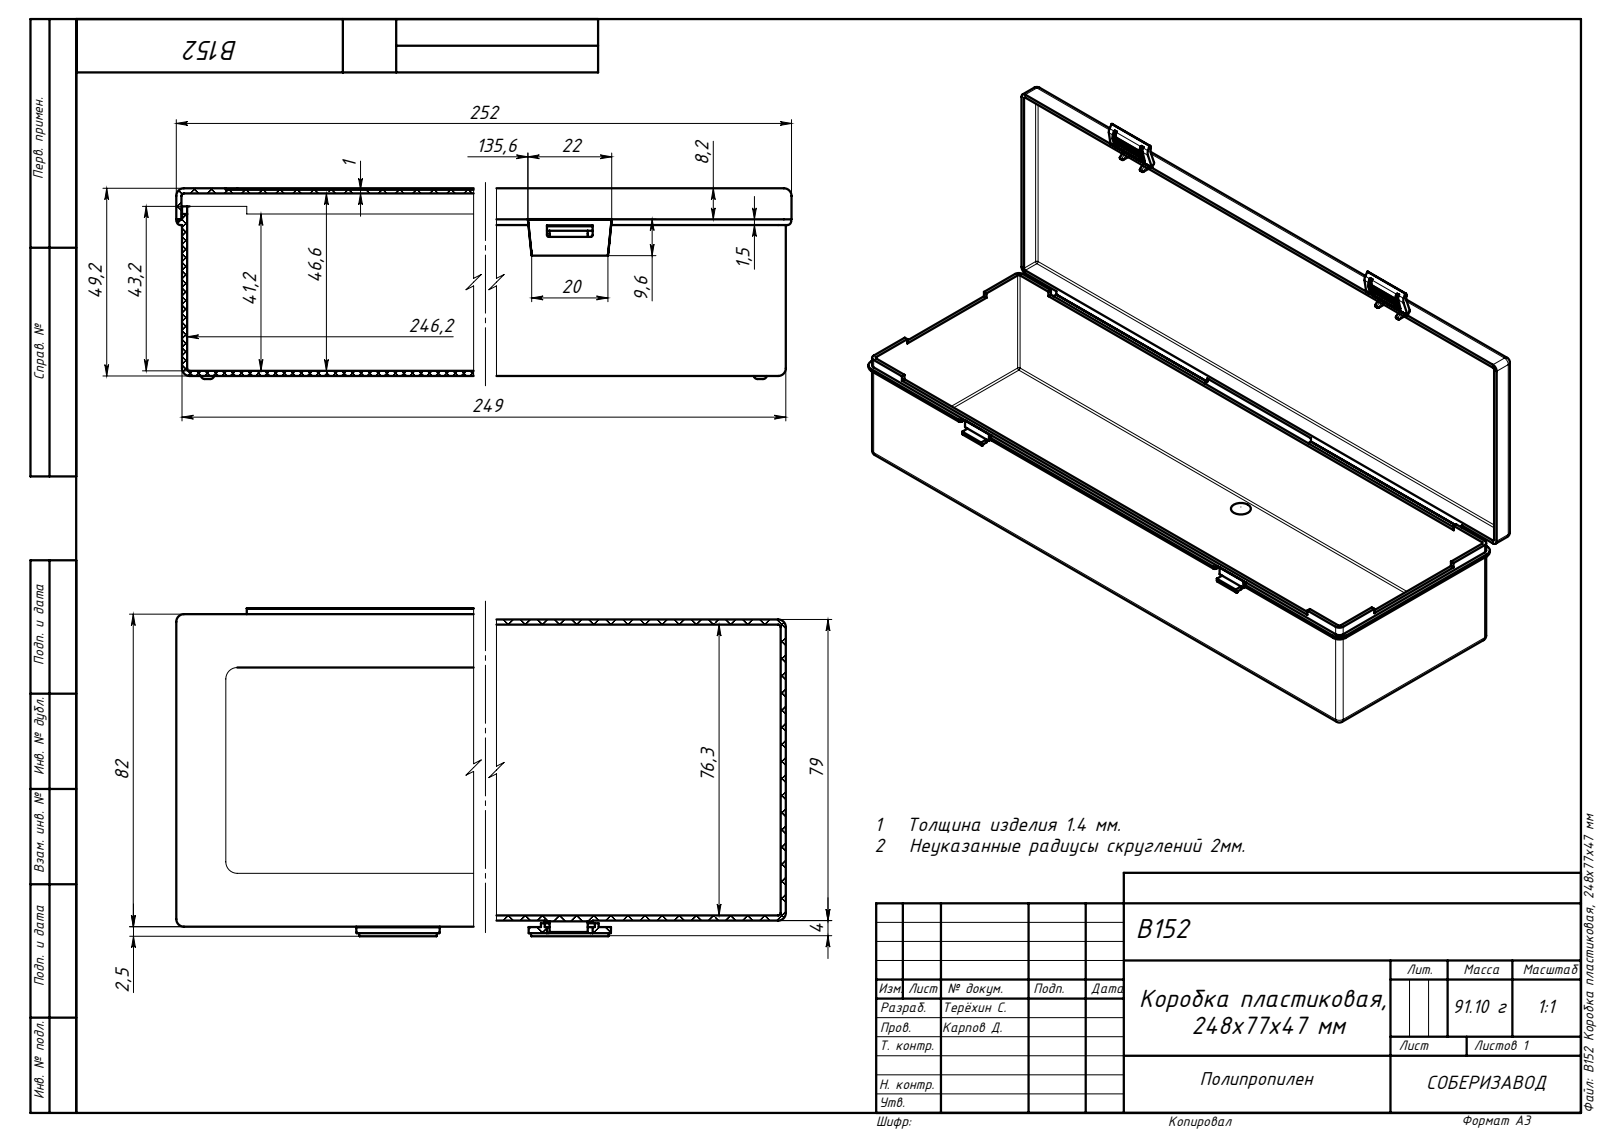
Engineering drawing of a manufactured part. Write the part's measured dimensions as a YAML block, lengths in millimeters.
part_name: "B152 Емкость_00; B152 Коробка пластиковая, 248x77x47 мм; B152 Крышка_12; B152 Защёлка_00"
step_written_by: "SolidWorks 2019 (CONFIG_CONTROL_DESIGN)"
units: millimeters
bodies: {solids: 13, faces: 349, planar: 187, cylindrical: 108, other: 54}
overall_size: [252, 86.01, 50.05]
volume: 93140
surface_area: 148248
partial_cylinders:
  - {radius: 0.5, count: 22}
  - {radius: 0.65, count: 16}
  - {radius: 2, count: 16}
  - {radius: 1.3, count: 8}
  - {radius: 1, count: 5}
  - {radius: 3, count: 4}
  - {radius: 3.4, count: 4}
  - {radius: 0.2, count: 1}
face_to_face_distances: [1.35, 47.9, 77.65, 46.55, 48.85, 47.5, 0.95, 76.3, 79, 0.4]
